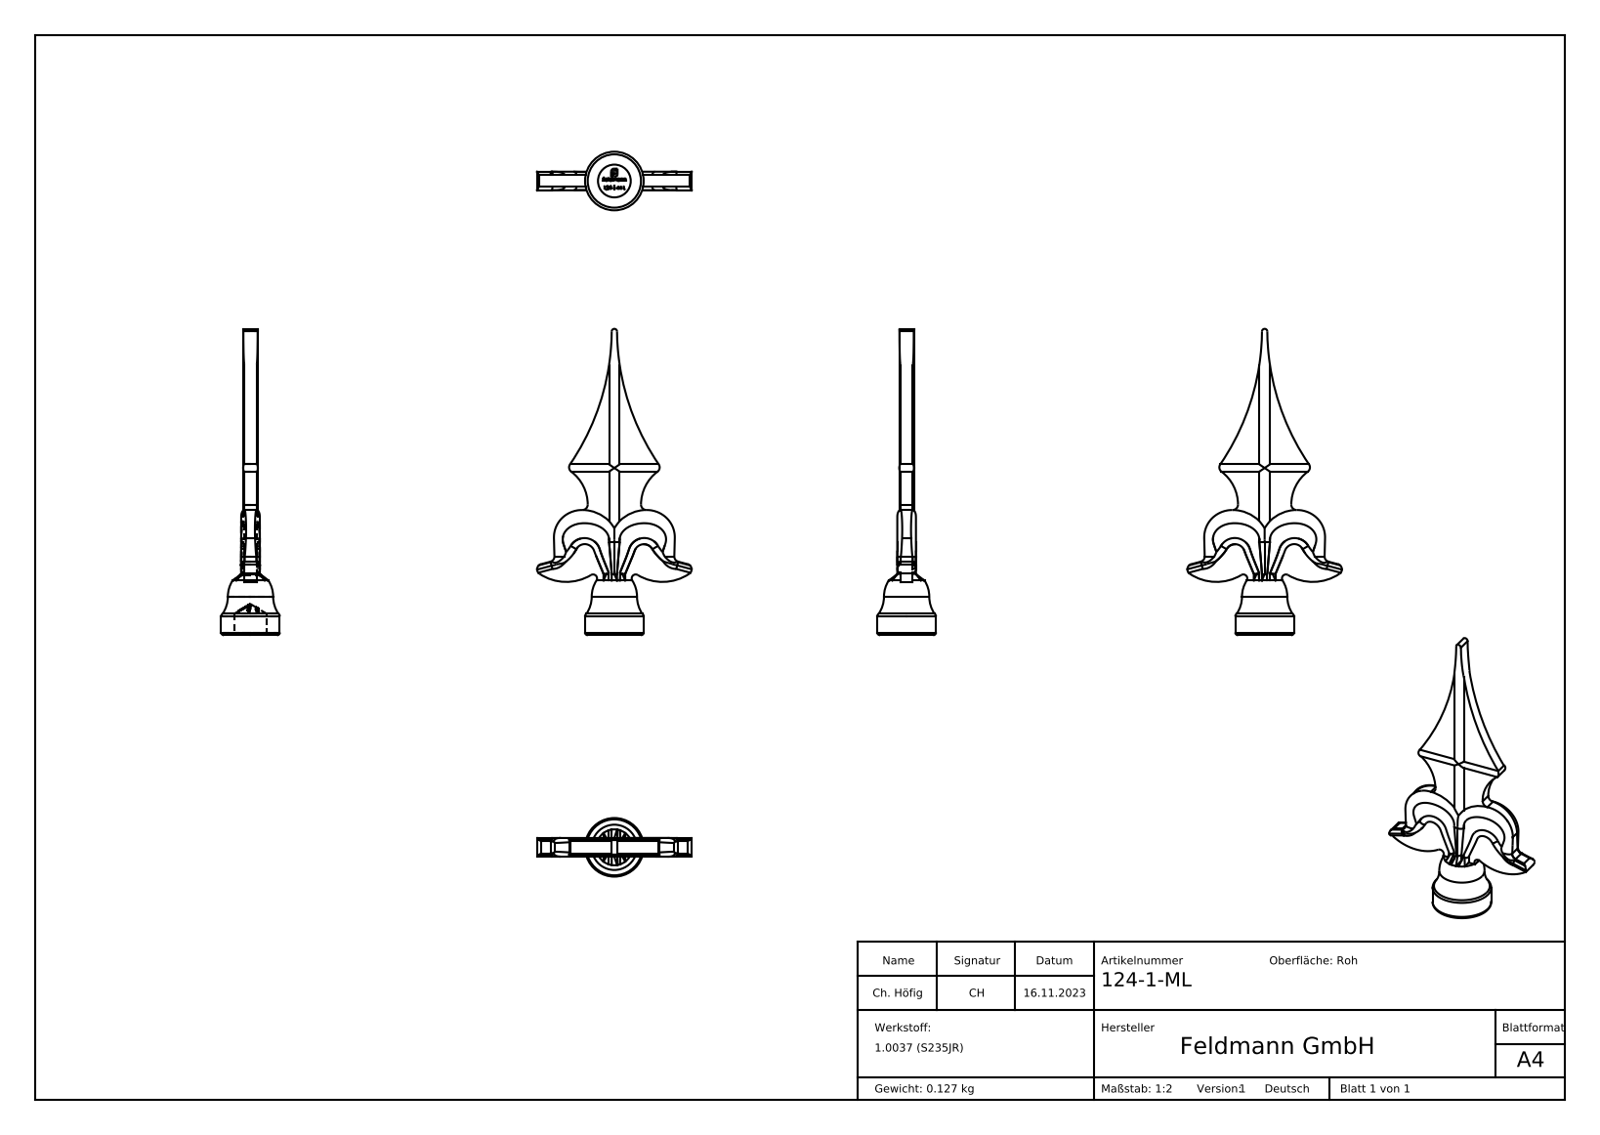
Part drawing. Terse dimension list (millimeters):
name: 124-1-ML
written by: SolidWorks 2018 (CONFIG_CONTROL_DESIGN)
unit: mm
bodies: 1 solid, 379 faces (167 planar, 21 cylindrical, 191 other)
size: 115 × 58 × 22
volume: 16 019 mm³; area: 8 148 mm²
holes: 1× ⌀12.3
bosses: 1× ⌀22
rounds: 8× R2, 2× R1.5, 2× R10.5, 2× R15.5, 2× R18, 2× R90, 1× R1
face distances: 4.5, 20.49, 45, 0.44, 2.34, 0.57, 0.75, 0.97, 3.27, 0.32
